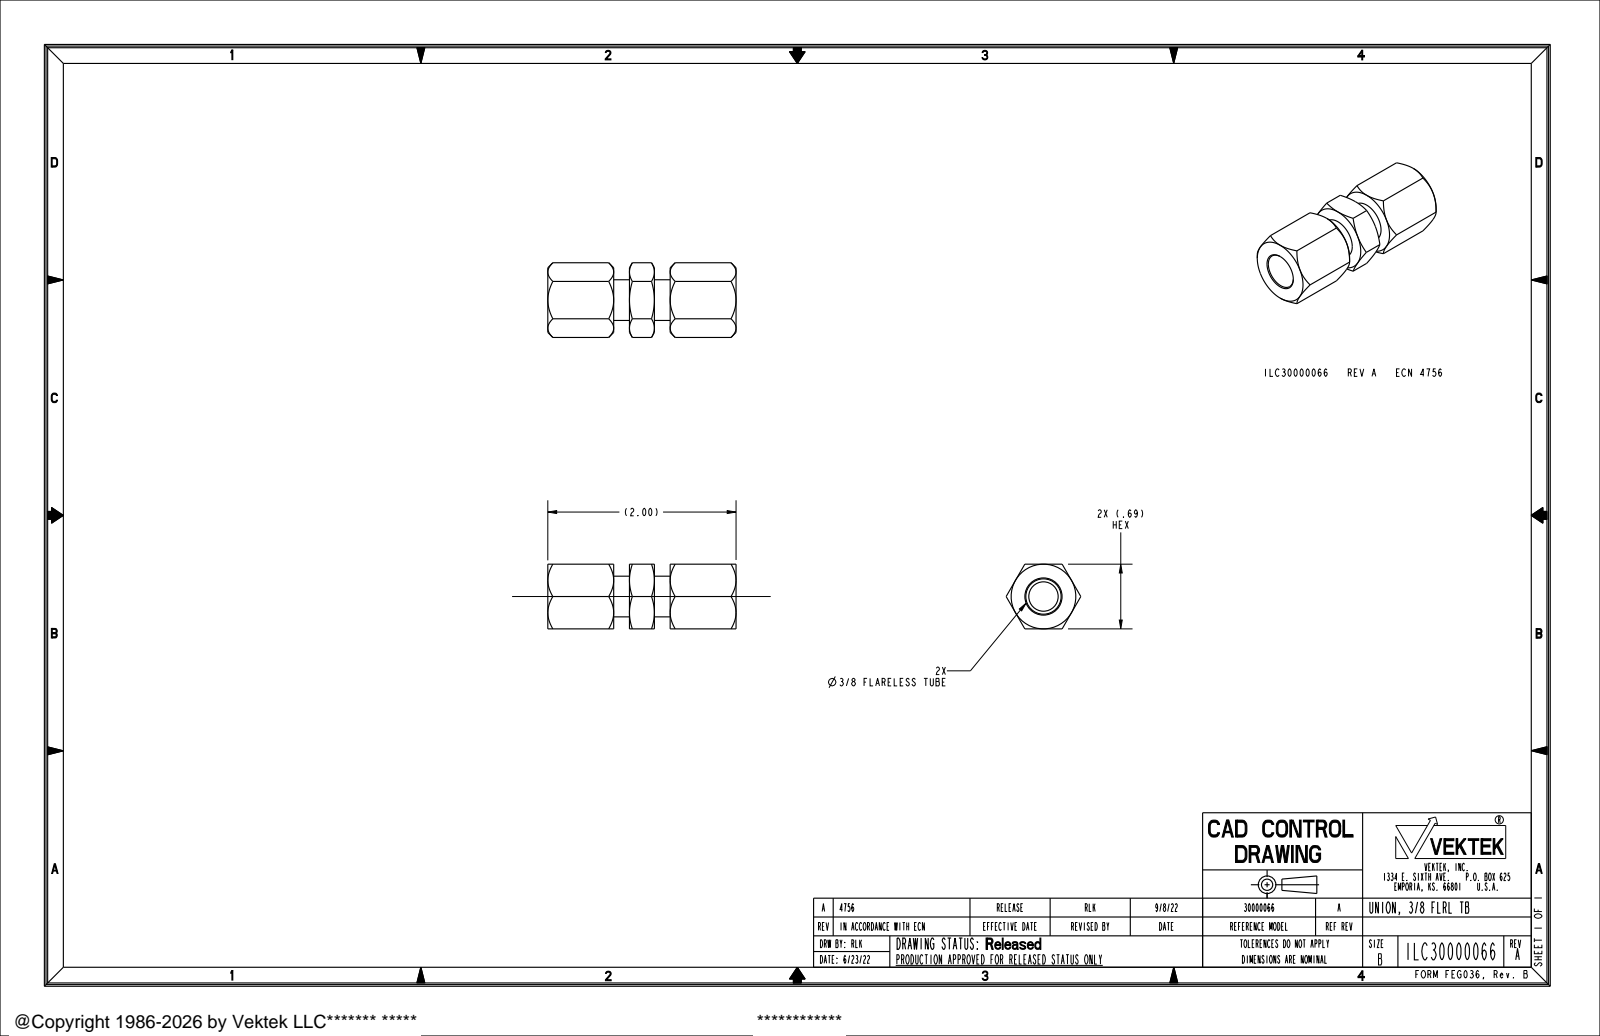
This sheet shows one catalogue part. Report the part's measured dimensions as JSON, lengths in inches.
{"part_name": "ILC30000066", "step_written_by": "CREO PARAMETRIC BY PTC INC, 2021164 (AUTOMOTIVE_DESIGN)", "units": "inches", "bodies": {"solids": 1, "faces": 76, "planar": 26, "cylindrical": 10, "other": 40}, "overall_size": [2, 0.793, 0.687], "volume_in3": 0.529, "surface_area_in2": 8.186, "round_holes": [[0.312, 1], [0.375, 1]], "round_bosses_or_shafts": [[0.432, 1]], "face_to_face_distances": [0.687, 0.7, 0.867, 1.133, 1.3, 0.167, 0.433, 2, 0.265, 0.6]}
